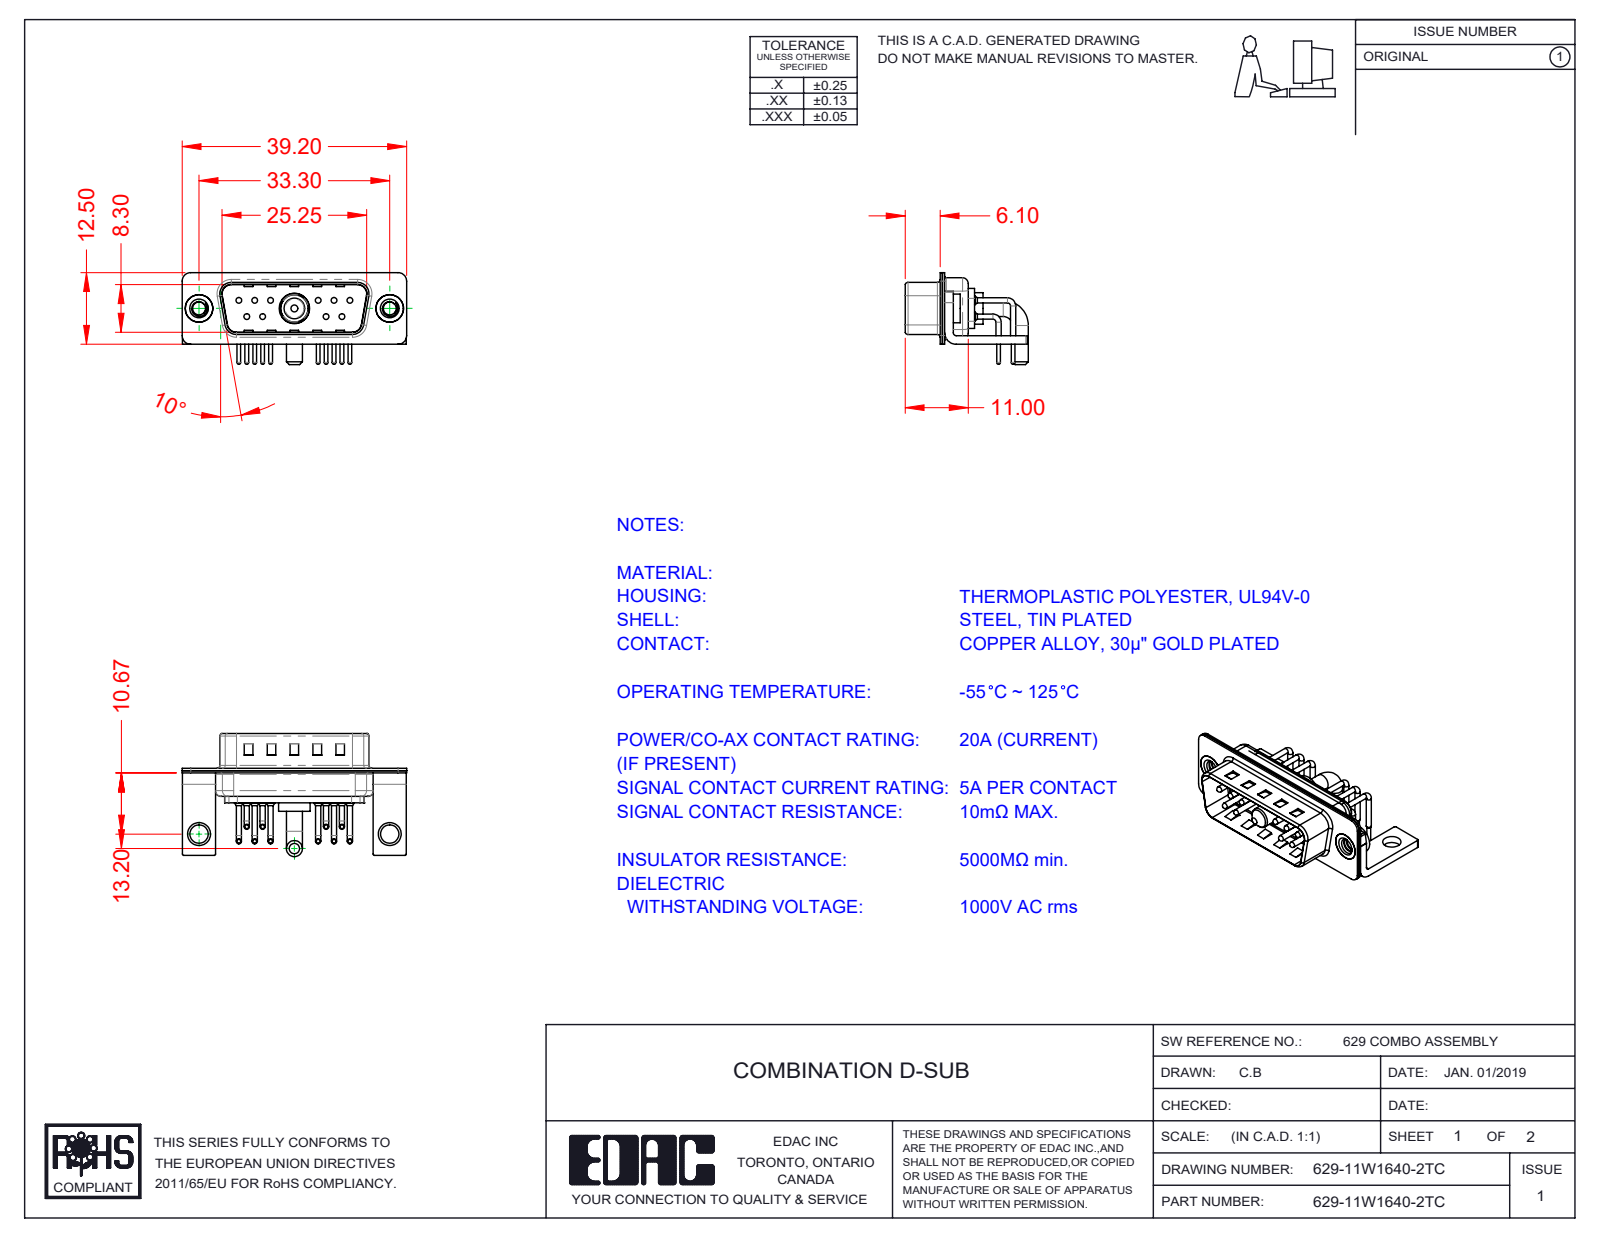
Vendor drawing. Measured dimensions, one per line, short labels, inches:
name: 629Combo Contact Row 1; 629-11W1640-2TC; 629Combo Shell Rear_15 Contacts; 629Combo Housing_11W1 (+5 more)
written by: SolidWorks 2020 (CONFIG_CONTROL_DESIGN)
unit: in
bodies: 19 solids, 1544 faces (818 planar, 542 cylindrical, 184 other)
size: 1.543 × 0.846 × 0.632
volume: 0.145 in³; area: 9.108 in²
holes: 10× ⌀0.03, 10× ⌀0.063, 10× ⌀0.079, 2× ⌀0.089, 2× ⌀0.126, 2× ⌀0.157, 2× ⌀0.189, 1× ⌀0.191, 1× ⌀0.209
bosses: 20× ⌀0.035, 10× ⌀0.059, 10× ⌀0.039, 10× ⌀0.026, 2× ⌀0.197, 2× ⌀0.193, 2× ⌀0.11, 1× ⌀0.217
rounds: 16× R0.01, 16× R0.059, 13× R0.079, 10× R0.04, 9× R0.02, 8× R0.063, 7× R0.039, 4× R0.024
face distances: 0.016, 0.031, 0.059, 0.374, 0.358, 0.024, 0.343, 0.39, 0.047, 0.205
hole spacings: 0.124, 0.109, 0.545, 0.436, 0.654, 0.198, 0.198, 0.218
